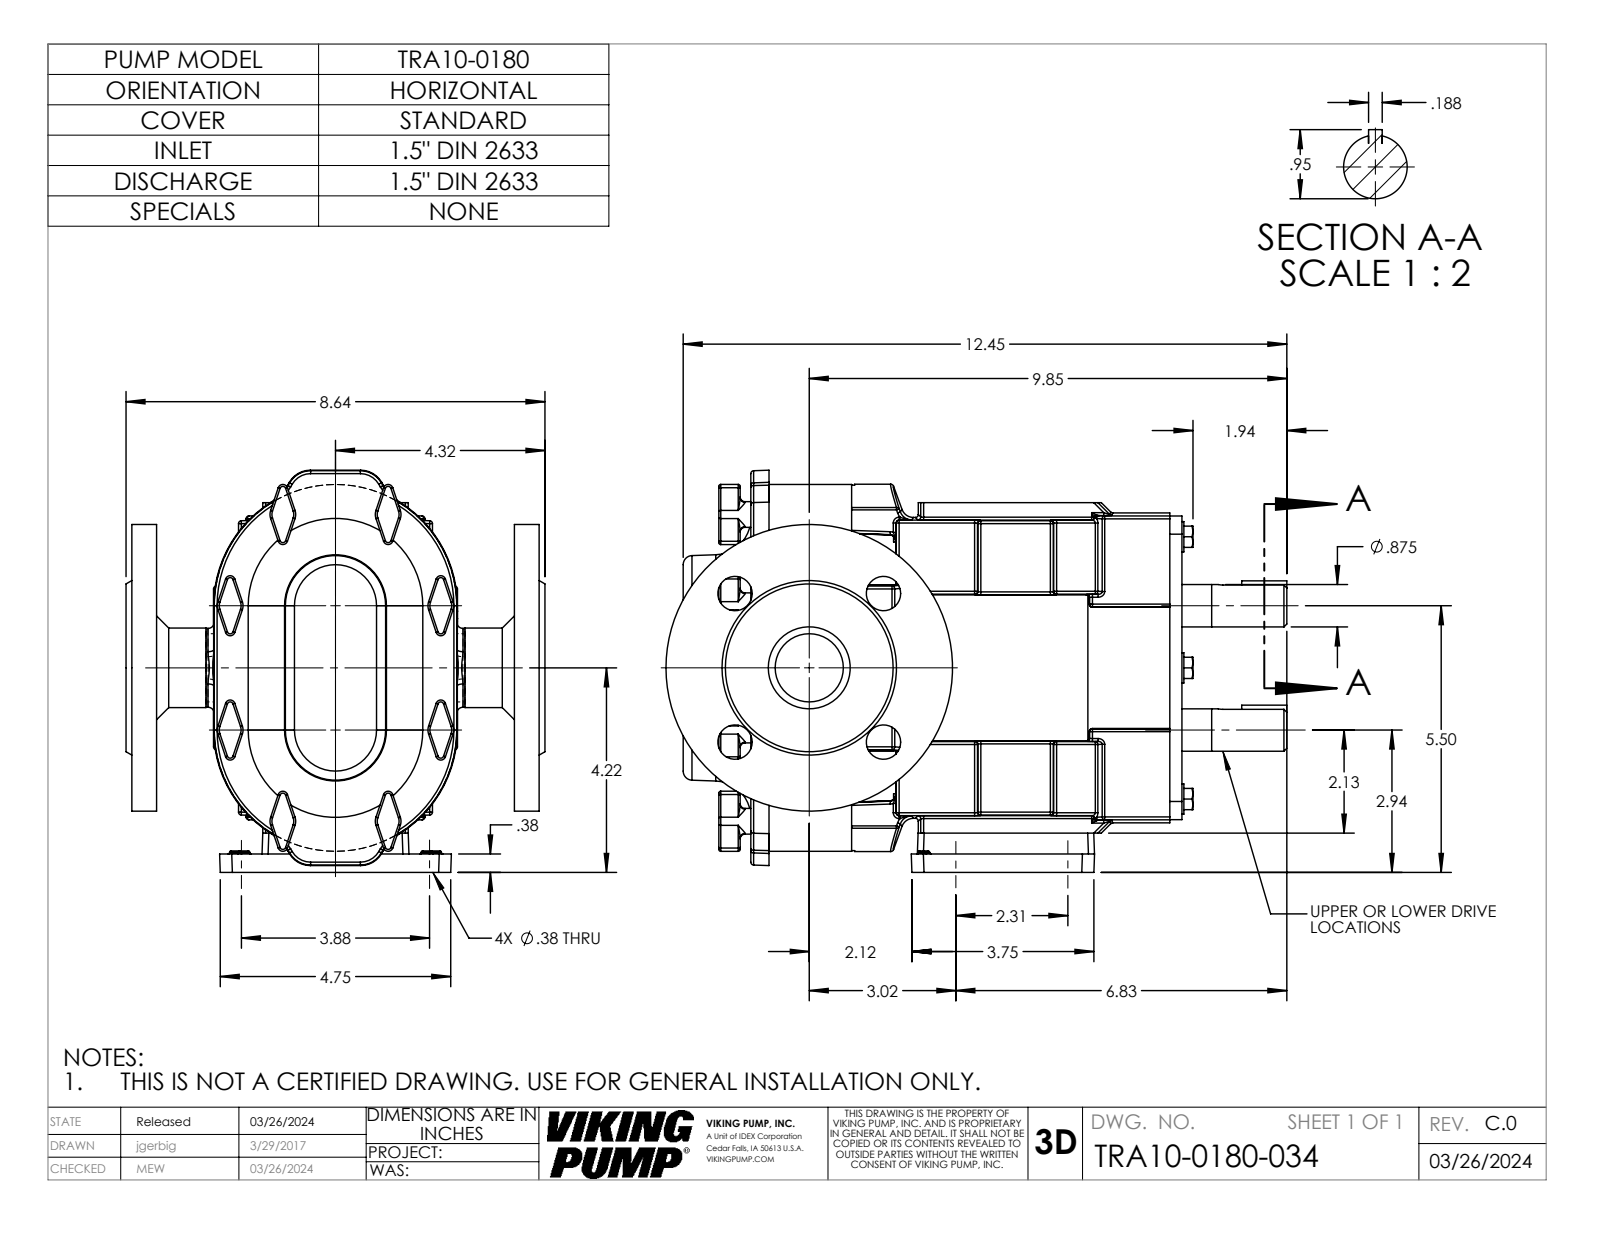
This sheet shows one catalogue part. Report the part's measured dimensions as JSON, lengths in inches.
{"part_name": "TRA10-0150-COVER-STD; TRA10-0180-BODY; TRA10-0150-GEARBOX-H; TRA10-0180-034 (+1 more)", "step_written_by": "SolidWorks 2022 (AUTOMOTIVE_DESIGN)", "units": "inches", "bodies": {"solids": 5, "faces": 1207, "planar": 321, "cylindrical": 465, "other": 421}, "overall_size": [12.805, 8.64, 8.292], "volume_in3": 274.5, "surface_area_in2": 624.7, "round_holes": [[0.375, 4], [0.709, 4], [1.406, 1], [1.69, 1]], "round_bosses_or_shafts": [[0.53, 8], [0.625, 6], [0.874, 2], [5.91, 1], [1.64, 1], [1.625, 1]], "partial_cylinders_radius": [[0.06, 189], [0.04, 64], [0.125, 20], [0.03, 16], [0.1, 16], [0.25, 14], [0.375, 4], [0.5, 4]], "face_to_face_distances": [1.704, 0.51, 7.89, 7.38, 2.075, 6.325, 1.565, 5.815, 8.517, 6.813], "hole_center_spacings": [2.165, 3.062, 2.31, 3.88, 4.331, 4.516]}
